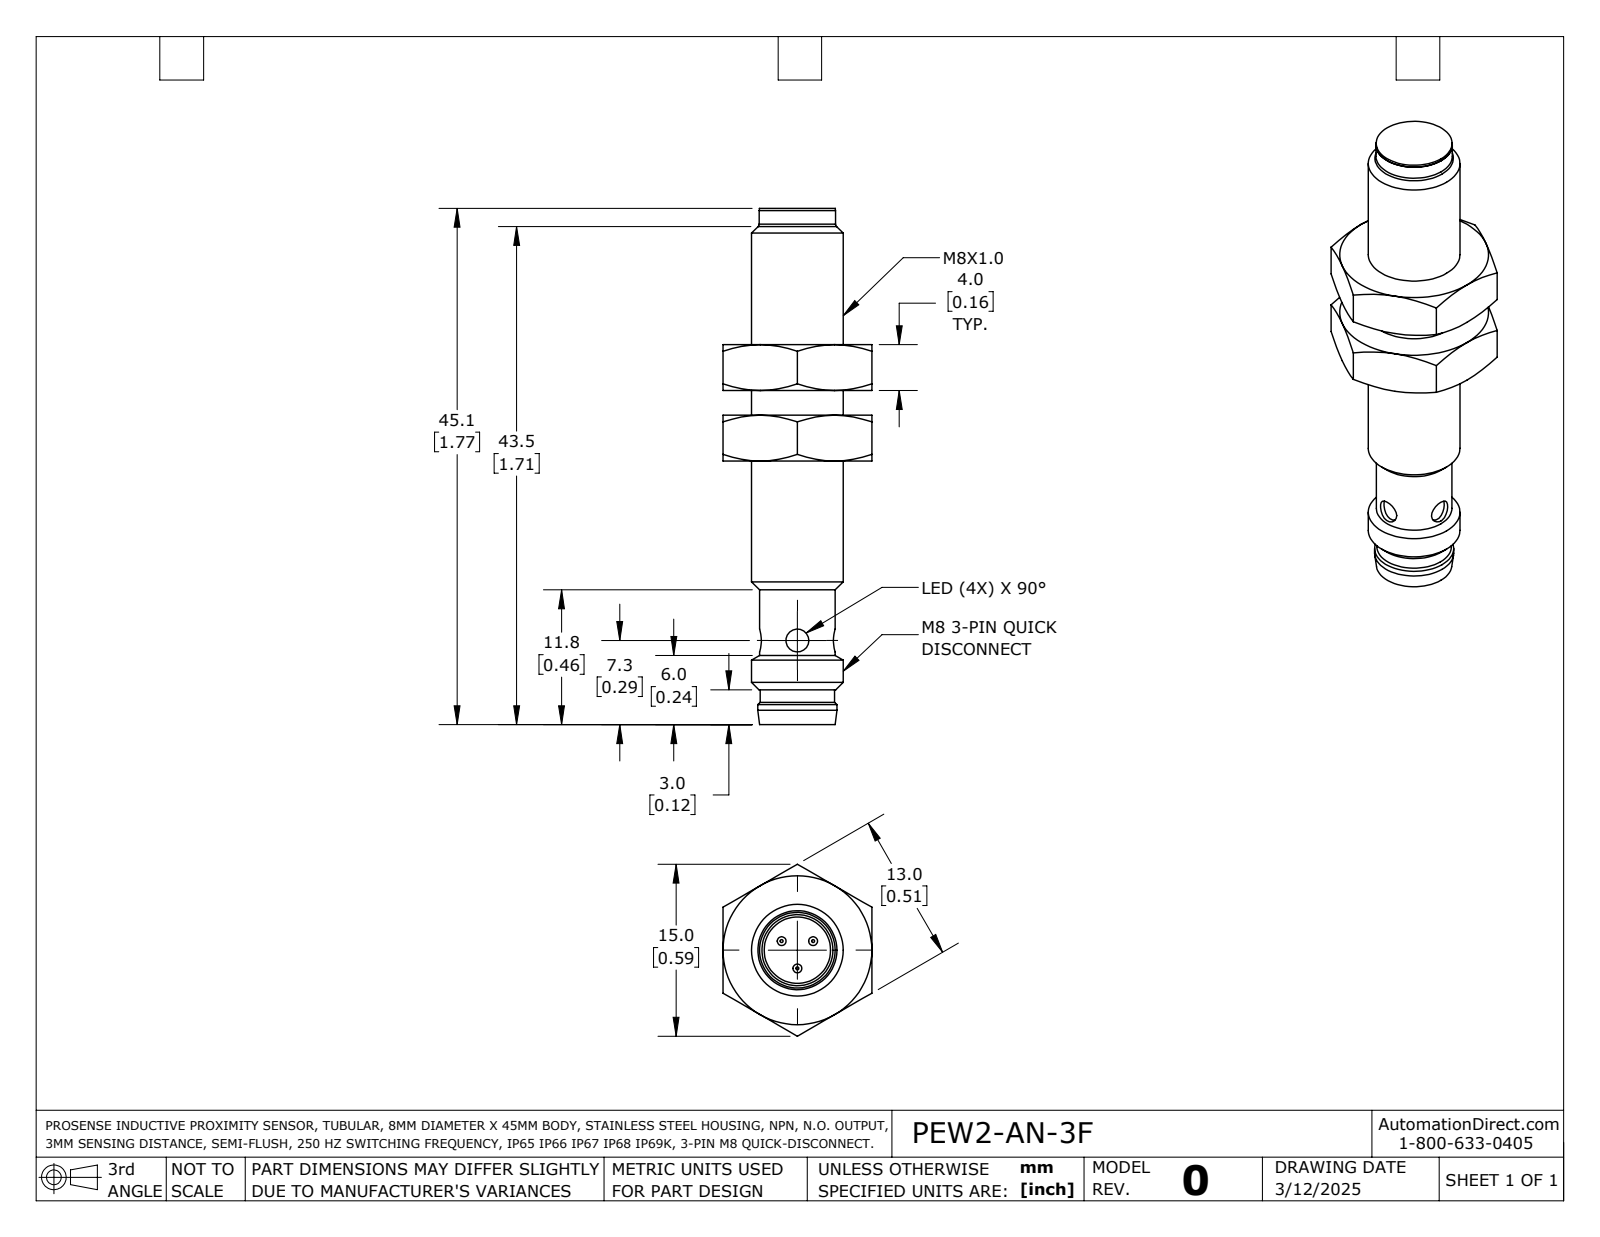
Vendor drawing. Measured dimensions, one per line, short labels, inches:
name: PEW2-AN-3F
written by: SolidWorks 2024 (AUTOMOTIVE_DESIGN)
unit: in
bodies: 3 solids, 75 faces (21 planar, 18 cylindrical, 36 other)
size: 1.774 × 0.591 × 0.512
volume: 0.17 in³; area: 3.41 in²
holes: 2× ⌀0.079, 1× ⌀0.272
bosses: 1× ⌀0.315, 1× ⌀0.272, 1× ⌀0.263, 1× ⌀0.261, 1× ⌀0.26, 1× ⌀0.256, 1× ⌀0.228
face distances: 0.243, 0.157, 0.512, 0.4, 0.085, 0.869, 0.711, 0.626, 0.469, 0.707
